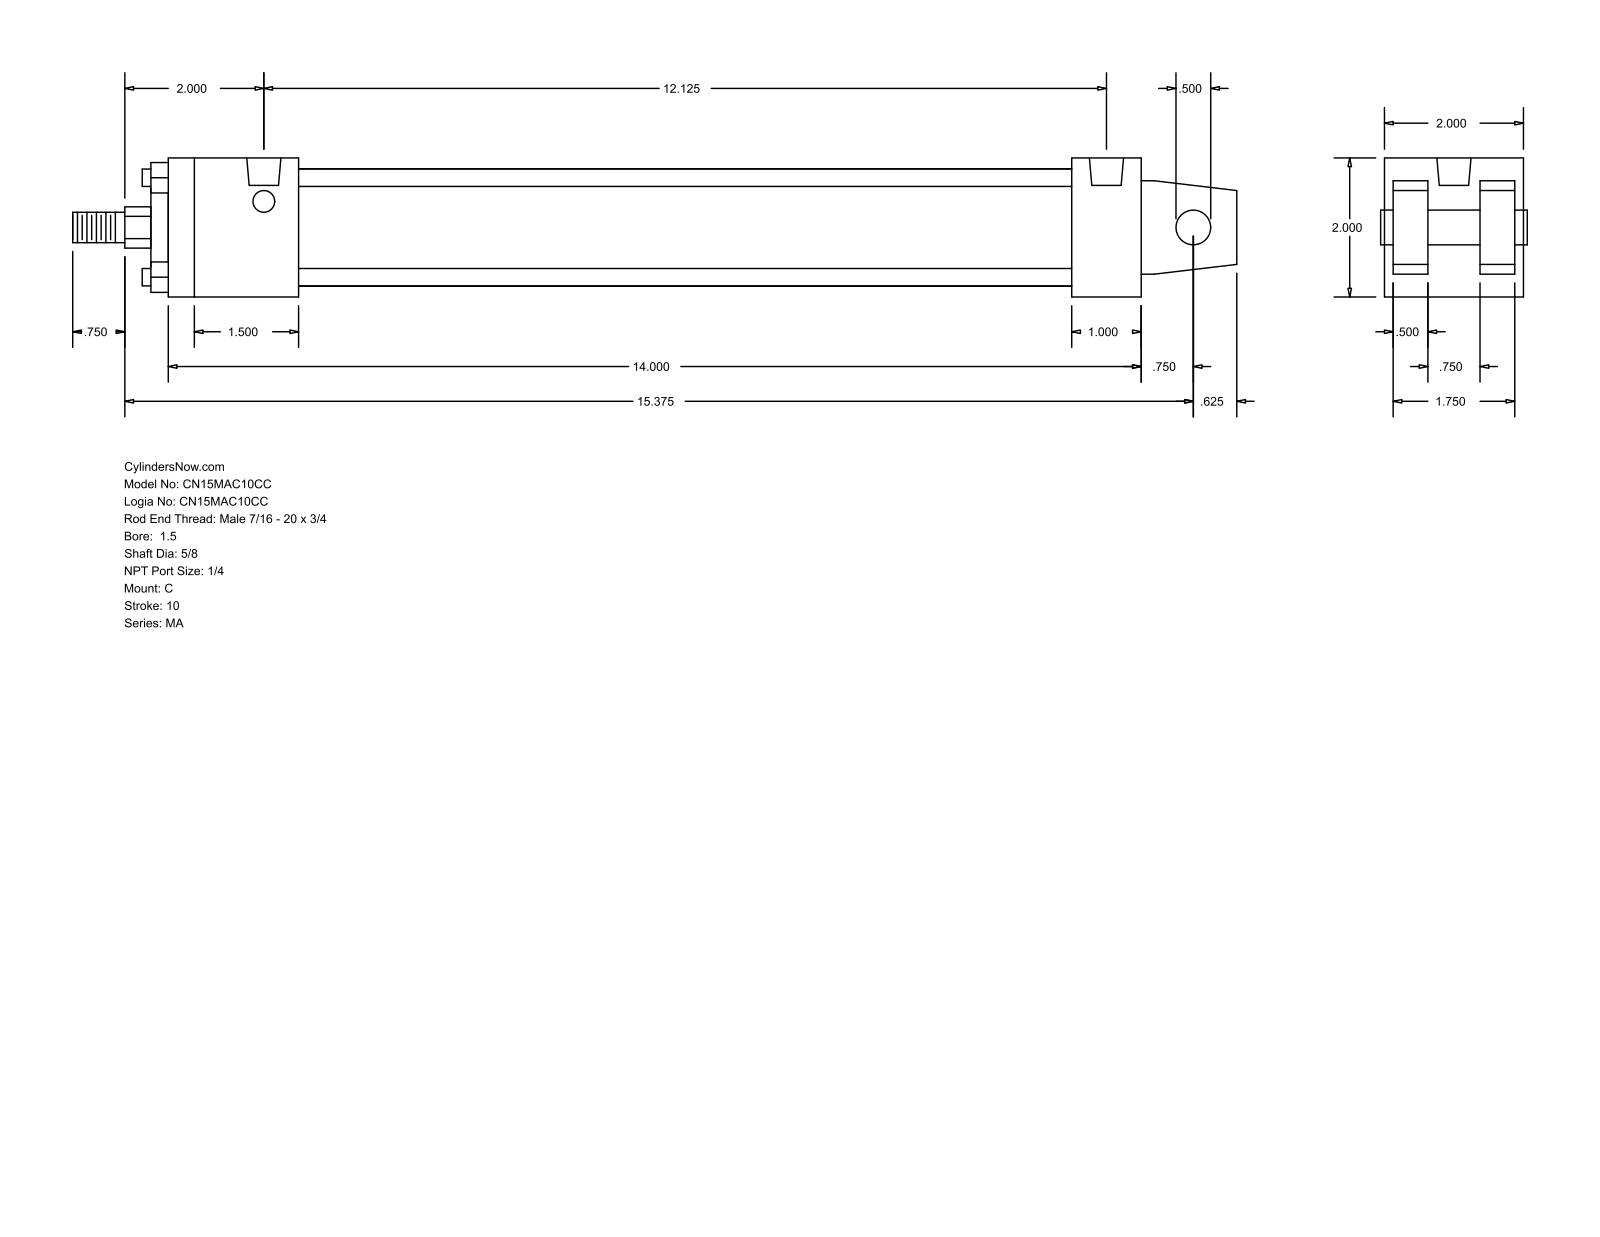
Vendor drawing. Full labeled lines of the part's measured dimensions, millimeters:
Part name (STEP PRODUCT): MA_C__0150_0.625
STEP written by: GSSL Pune (CONFIG_CONTROL_DESIGN)
Units: millimetres
Bodies: 0 solids, 103 faces (76 planar, 27 cylindrical, 0 other)
Overall size (bounding box): 425.45 × 50.8 × 50.8
Round holes (diameter × count): ⌀7.94 ×4, ⌀12.49 ×2
Round bosses / shafts (diameter × count): ⌀6.35 ×4, ⌀42.93 ×1, ⌀28.57 ×1, ⌀15.88 ×1, ⌀12.7 ×1, ⌀11.11 ×1
Partial cylindrical surfaces — rounded edges, fillets, slot ends (radius × count): R7.54 ×1
Main face-to-face distances: 50.8, 12.7, 34.93, 15.87, 3.17, 47.63, 31.76, 355.6, 330.19, 25.41
Hole centre spacings: 307.97
